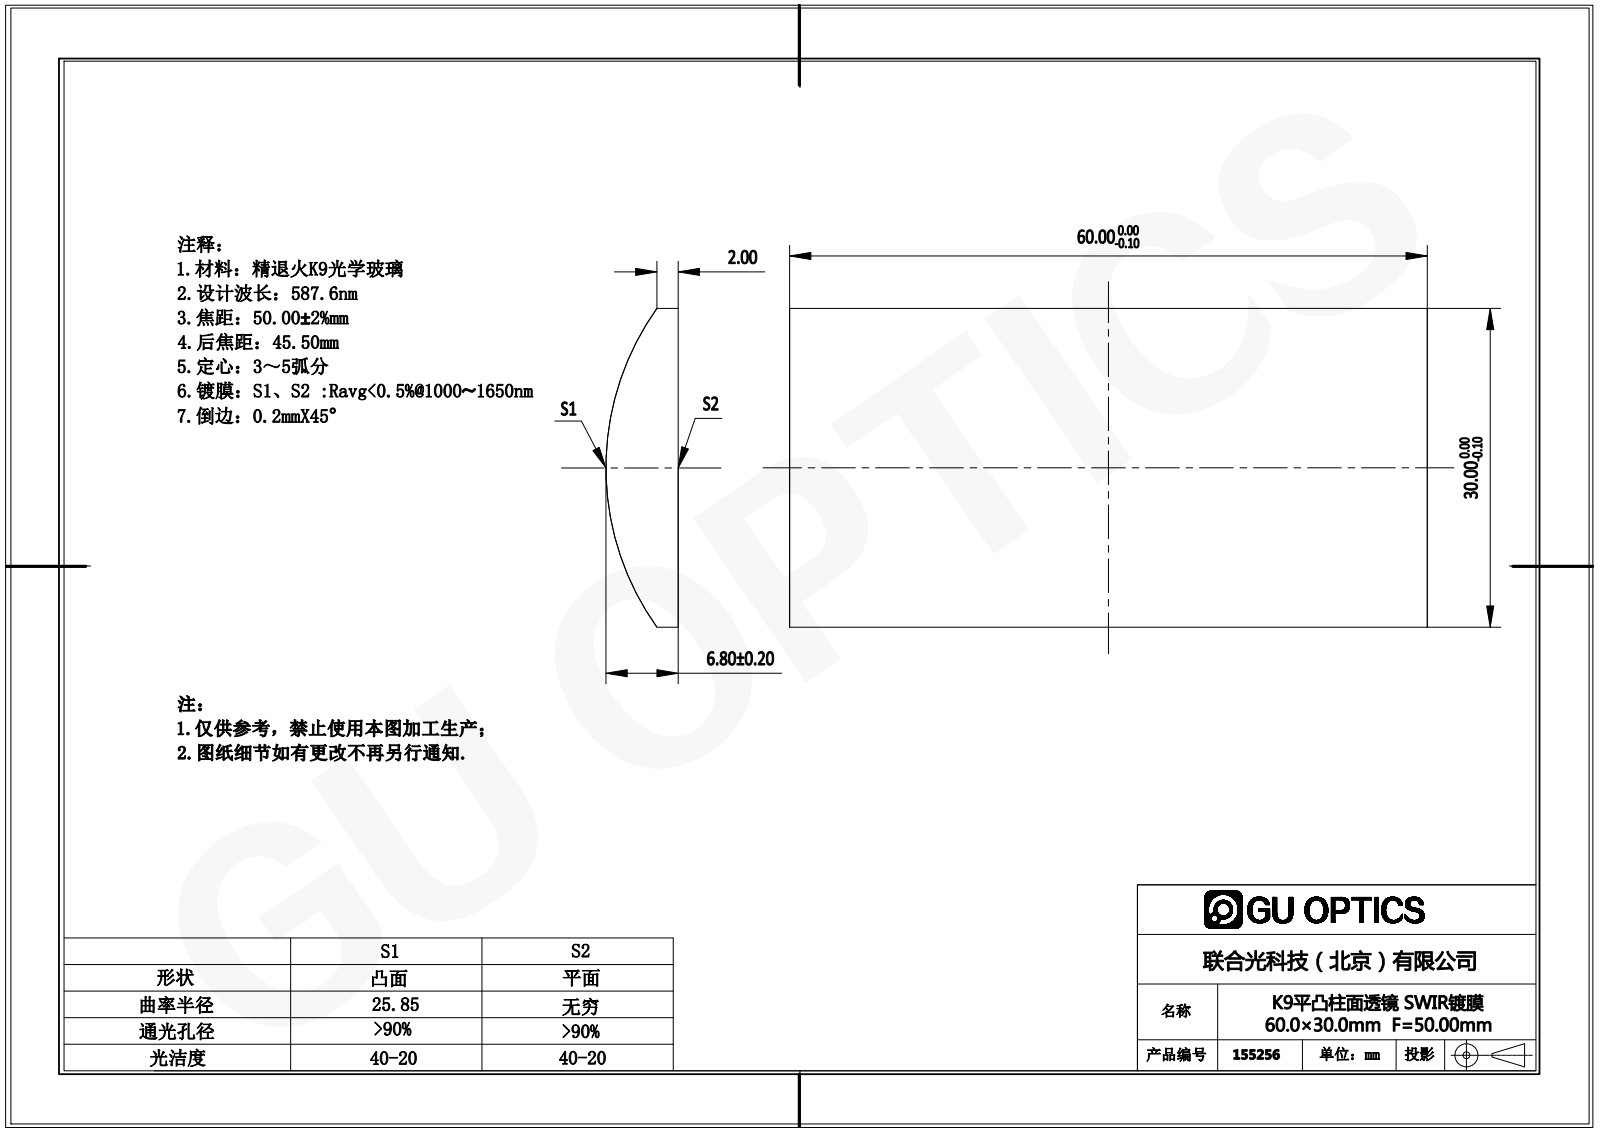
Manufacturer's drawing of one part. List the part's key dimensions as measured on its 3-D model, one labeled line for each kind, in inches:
Part name (STEP PRODUCT): 155058
STEP written by: SolidWorks 2016 (AUTOMOTIVE_DESIGN)
Units: inches
Bodies: 1 solid, 6 faces (5 planar, 1 cylindrical, 0 other)
Overall size (bounding box): 2.362 × 1.181 × 0.268
Volume: 0.578 in³ · Surface area: 6.629 in²
Partial cylindrical surfaces — rounded edges, fillets, slot ends (radius × count): R1.018 ×1
Main face-to-face distances: 2.362, 1.181
